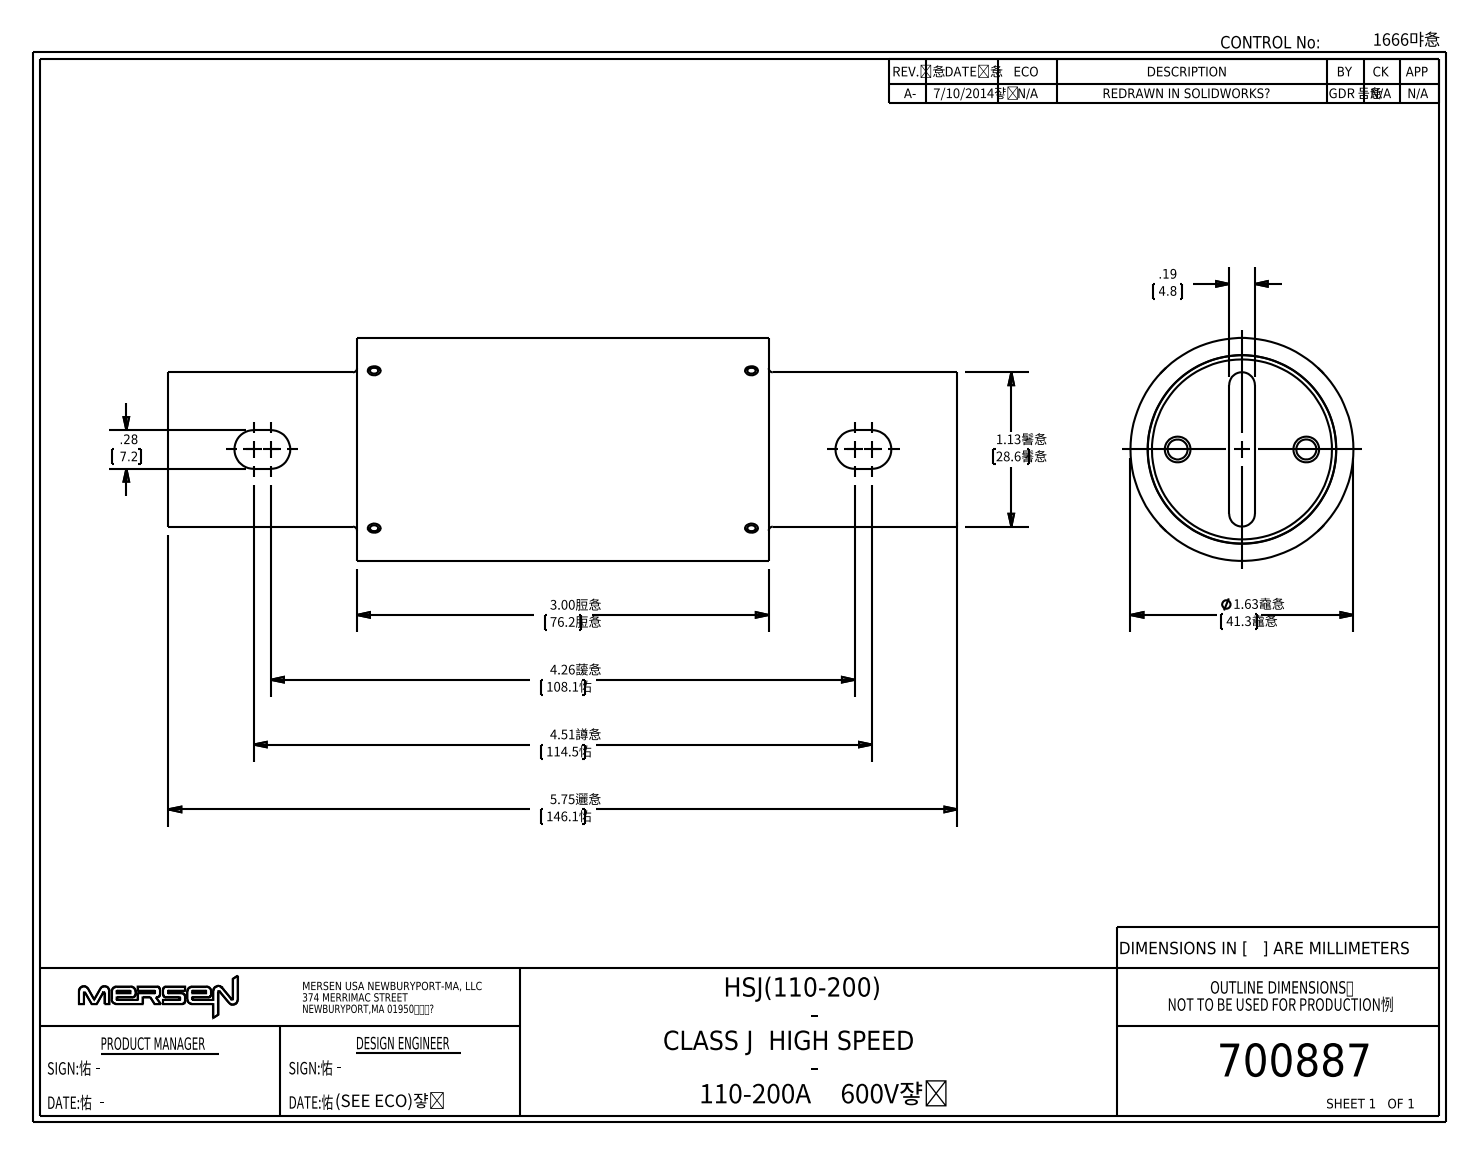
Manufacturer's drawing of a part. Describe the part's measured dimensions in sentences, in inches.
The part is named "700887revA". Its 3-D file was written by "SolidWorks 2013 (AUTOMOTIVE_DESIGN)". It is 0 solids with 133 faces: 48 planar, 50 cylindrical and 35 other. Overall it measures 5.75 by 1.625 by 1.625 inches. Round holes: 4 of diameter 0.094, 2 of diameter 0.188, 1 of diameter 1.375. Round bosses or shafts: 2 of diameter 0.146, 1 of diameter 1.625. Partial cylindrical surfaces (rounded edges, fillets, slot ends): 4 of radius 0.03, 4 of radius 0.141, 2 of radius 0.094. The main face-to-face distances are 0.187, 3, 1.375, 4.375, 5.75, 0.282, 1.624. The hole center spacings are 0.469, 2.75, 0.938.
